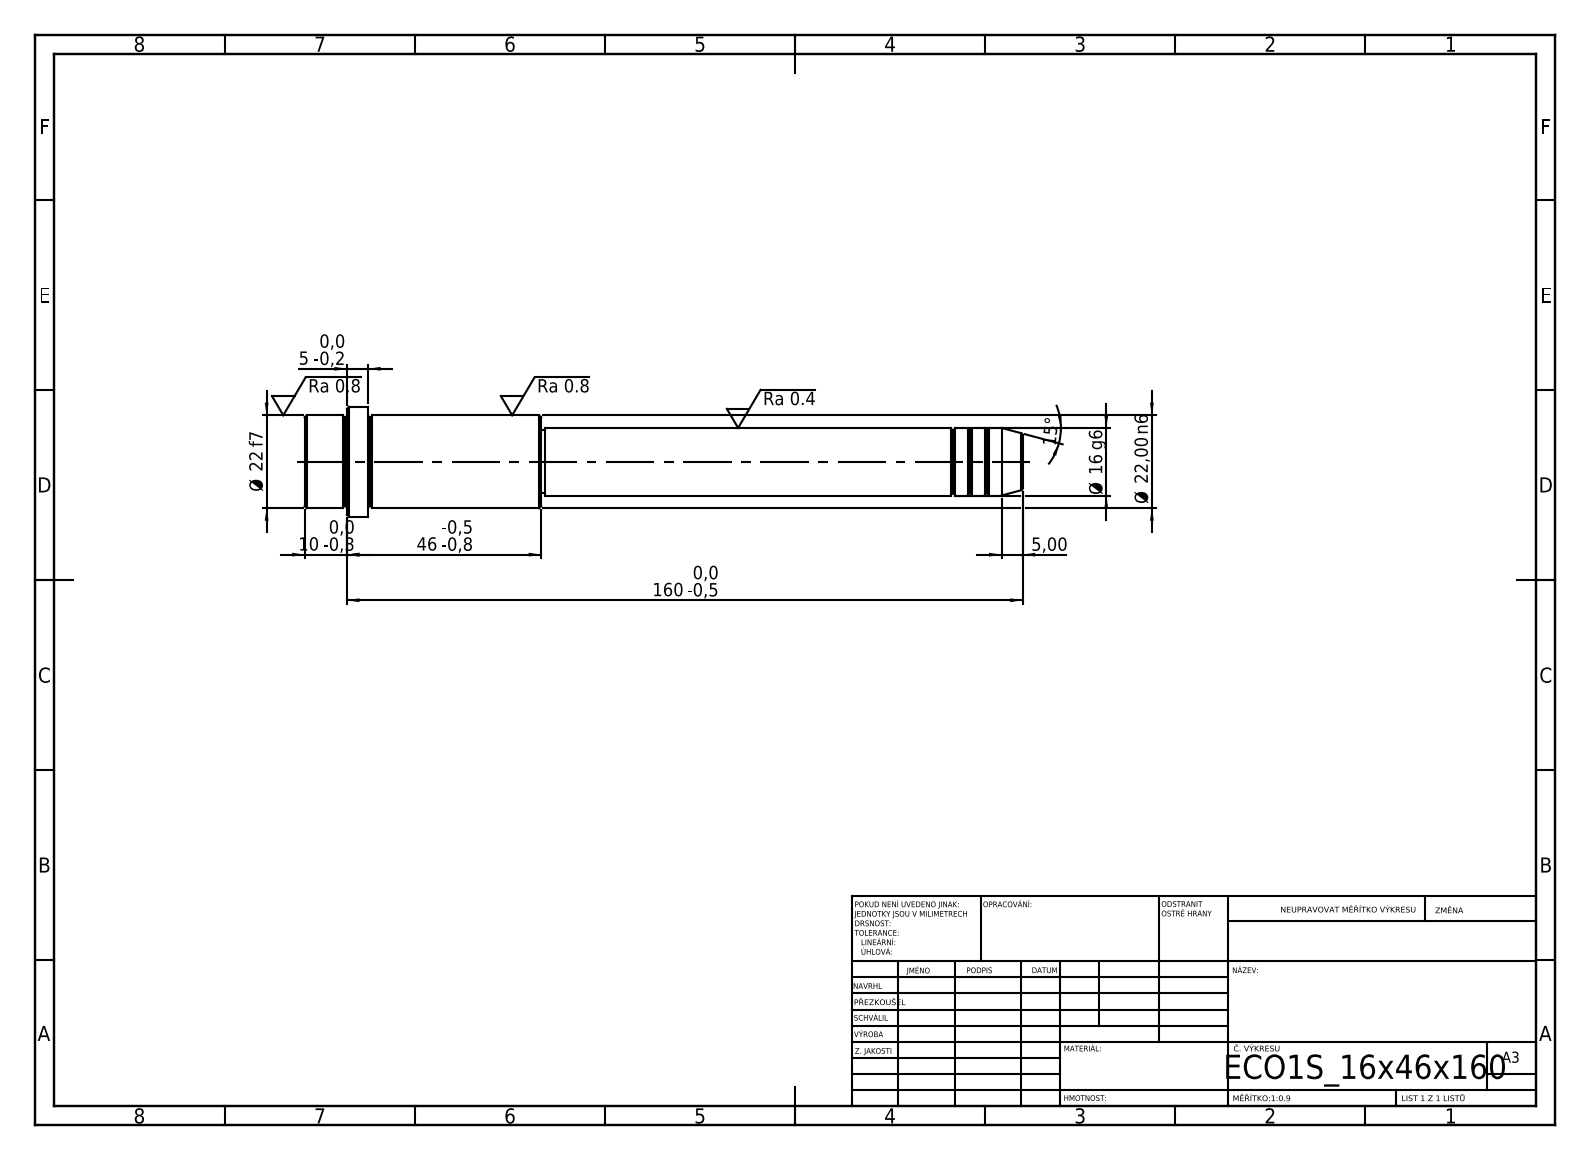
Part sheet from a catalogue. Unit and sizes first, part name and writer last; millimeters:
Units: millimetres
Overall size (bounding box): 170 × 26 × 26
Round bosses / shafts (diameter × count): ⌀26 ×1, ⌀22 ×1, ⌀16 ×1, ⌀15 ×1
Main face-to-face distances: 56, 41, 15, 114, 155, 170, 160, 46, 5, 10
Volume: 44 640 mm³ · Surface area: 10 775 mm²
Bodies: 1 solid, 52 faces (6 planar, 16 cylindrical, 30 other)
STEP written by: SolidWorks 2019 (CONFIG_CONTROL_DESIGN)
